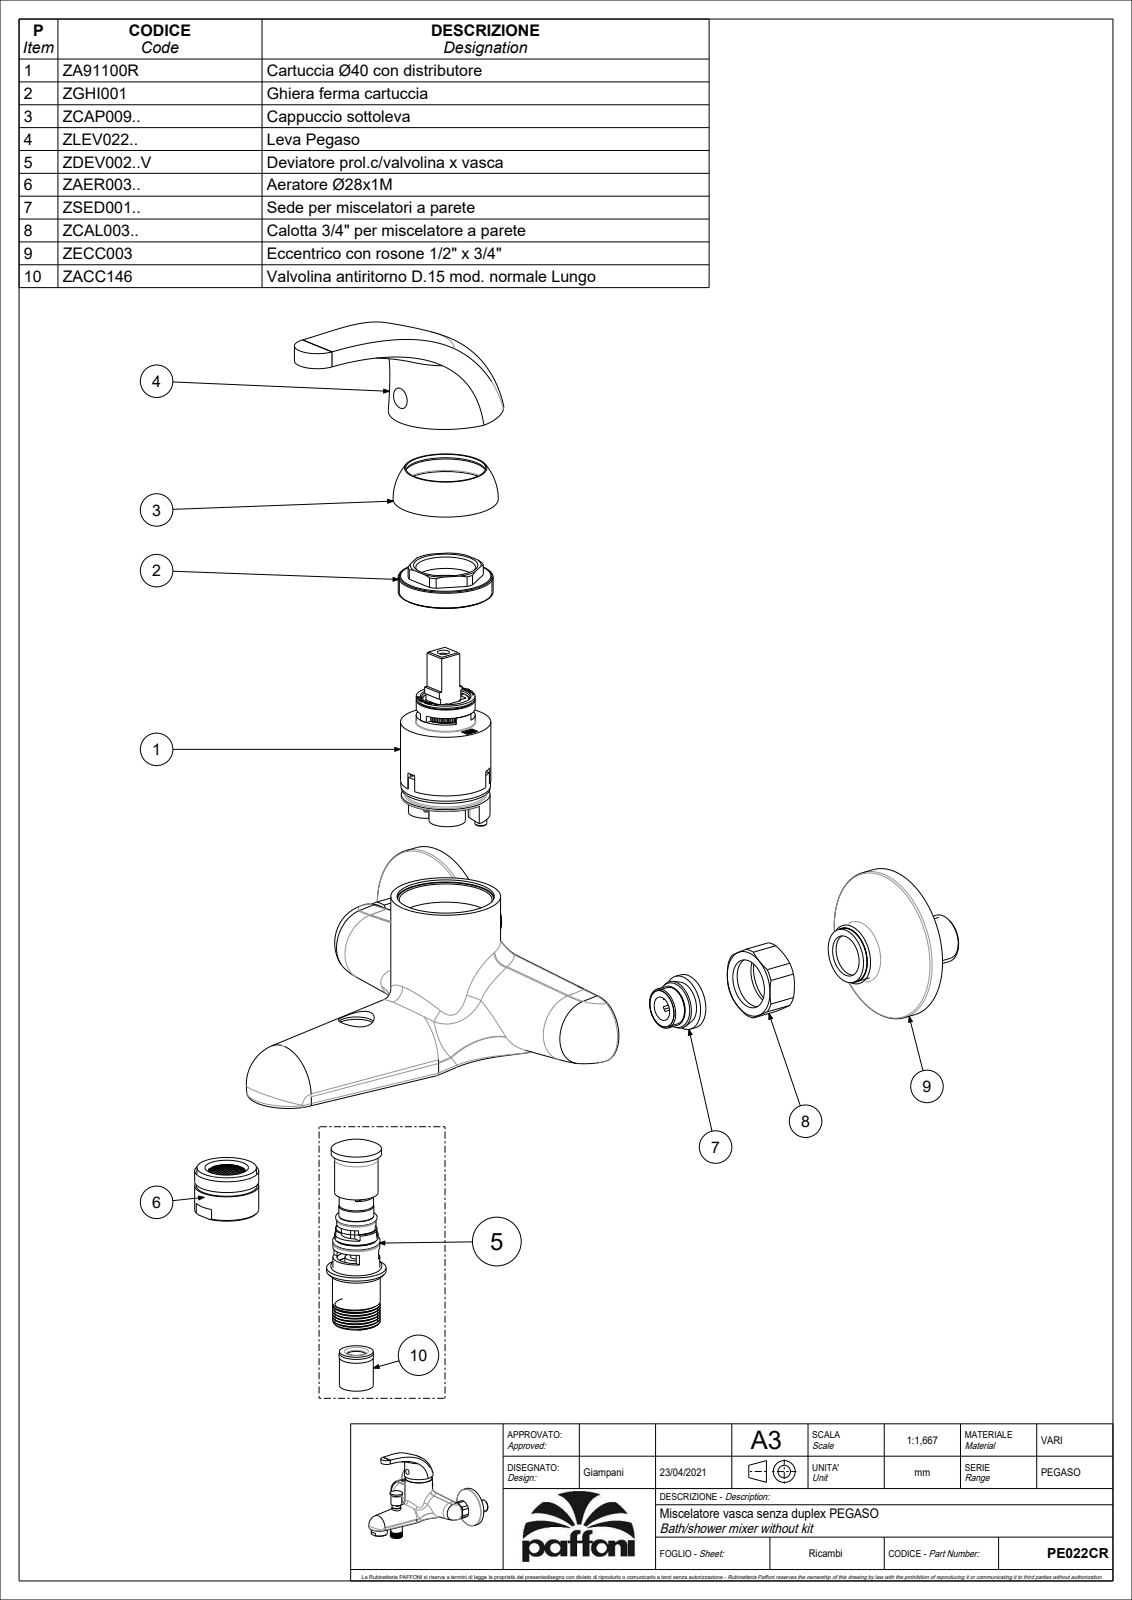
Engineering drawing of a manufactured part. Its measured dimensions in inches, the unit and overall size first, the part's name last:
Units: inches
Overall size (bounding box): 8.504 × 7.343 × 5.924
Round holes (diameter × count): ⌀1.051 ×2, ⌀0.236 ×1
Round bosses / shafts (diameter × count): ⌀2.598 ×2, ⌀1.039 ×2, ⌀0.827 ×2, ⌀1.89 ×1, ⌀1.102 ×1, ⌀1.024 ×1, ⌀0.866 ×1, ⌀0.823 ×1
Partial cylindrical surfaces — rounded edges, fillets, slot ends (radius × count): R0.039 ×8, R0.61 ×2, R0.807 ×2, R0.154 ×1
Main face-to-face distances: 1.339, 1.358, 0.02, 1.142, 3.386, 0.059, 1.299, 0.039, 4.3, 0.914
Hole centre spacings: 3.869, 5.906
Volume: 30.28 in³ · Surface area: 124.9 in²
Bodies: 1 solid, 346 faces (65 planar, 83 cylindrical, 198 other)
Part name (STEP PRODUCT): PE022CR_SW0001
STEP written by: CREO PARAMETRIC BY PTC INC, 2022124 (CONFIG_CONTROL_DESIGN)
